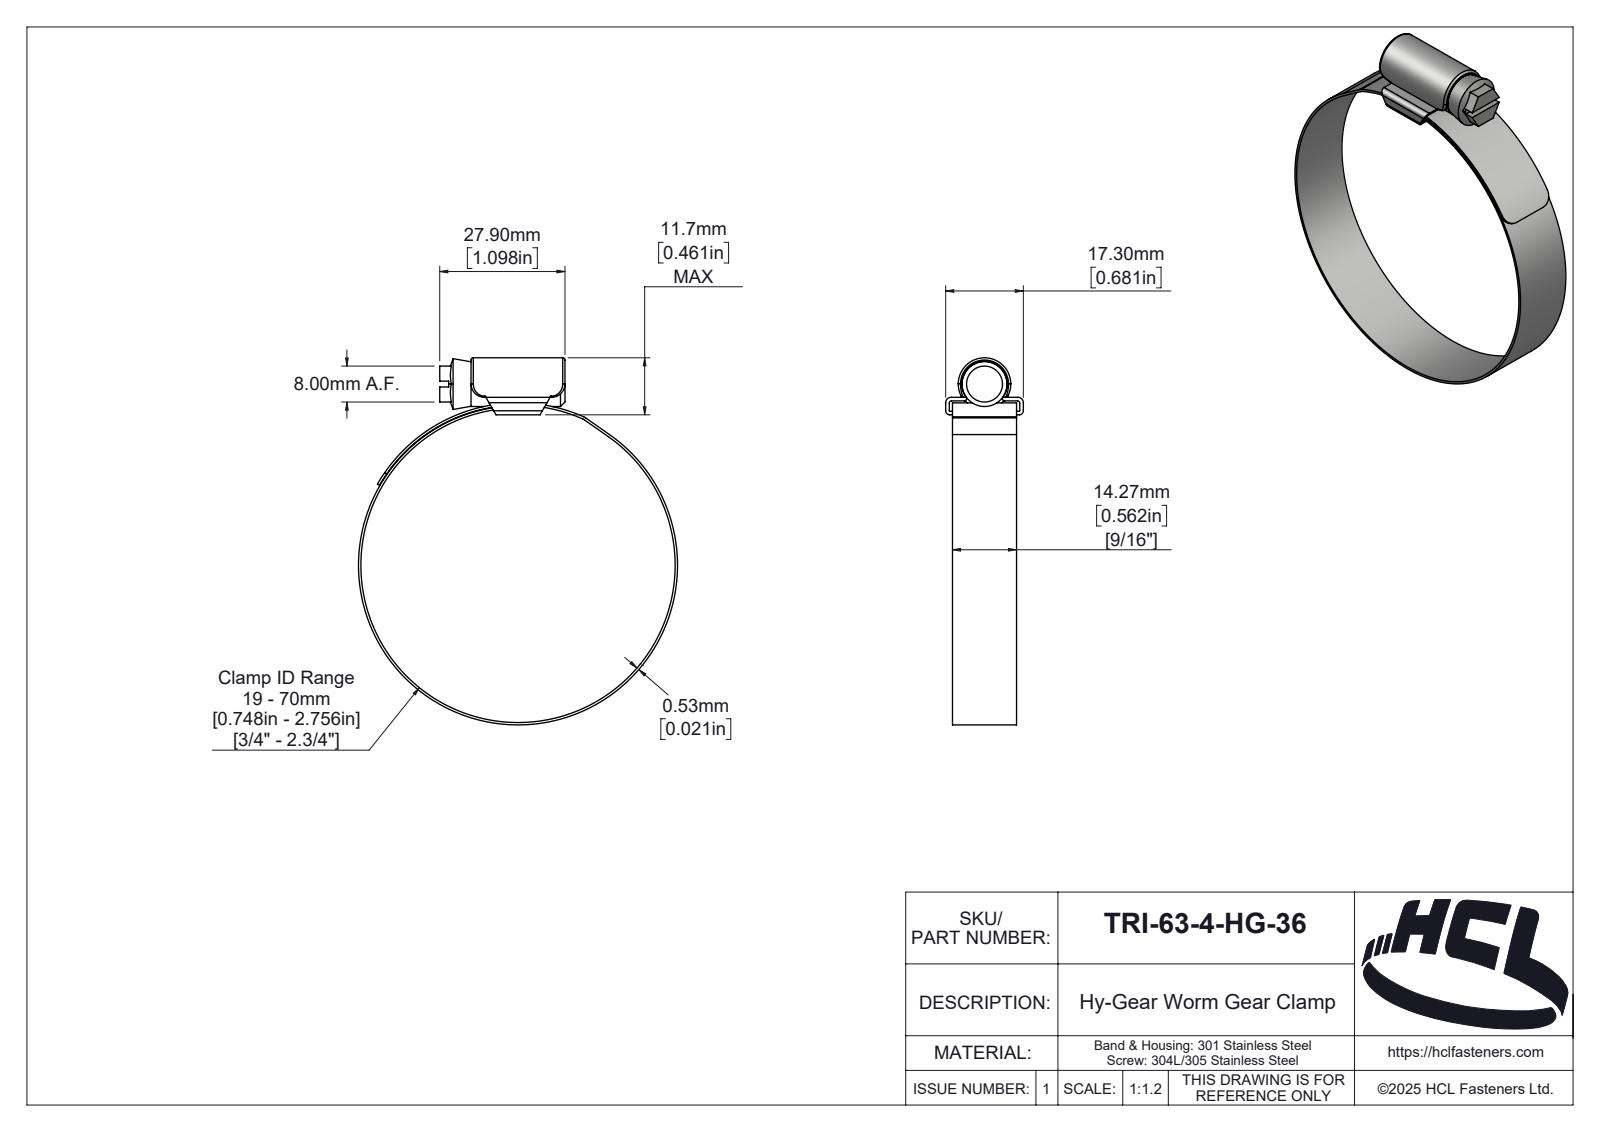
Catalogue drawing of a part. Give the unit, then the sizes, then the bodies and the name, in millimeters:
Units: millimetres
Overall size (bounding box): 81.73 × 71.06 × 17.3
Round holes (diameter × count): ⌀70 ×1
Round bosses / shafts (diameter × count): ⌀71.06 ×1, ⌀10 ×1
Partial cylindrical surfaces — rounded edges, fillets, slot ends (radius × count): R0.5 ×6, R3 ×4, R0.1 ×2, R0.9 ×2, R1.2 ×2, R0.46 ×1, R1.89 ×1, R2 ×1
Main face-to-face distances: 0.8, 3.1, 14.26, 2.3, 0.53, 3.9, 27.9, 1.52, 15.78, 16.5
Volume: 4 753 mm³ · Surface area: 10 480 mm²
Bodies: 3 solids, 189 faces (39 planar, 89 cylindrical, 61 other)
Part name (STEP PRODUCT): TRI-50-0-HG-36
STEP written by: SolidWorks 2025 (AUTOMOTIVE_DESIGN)
